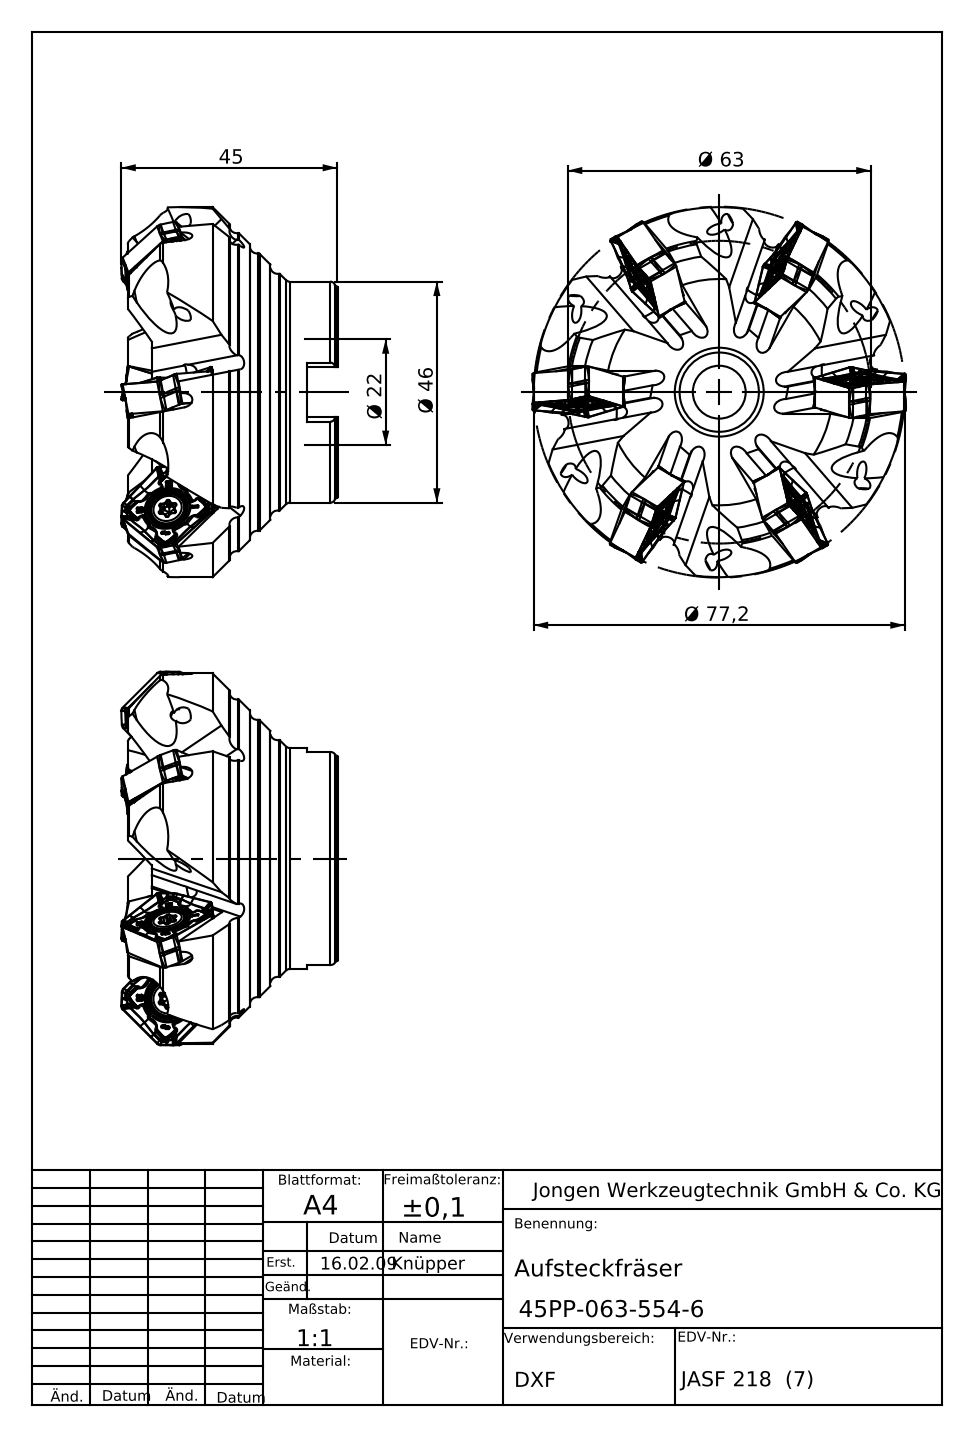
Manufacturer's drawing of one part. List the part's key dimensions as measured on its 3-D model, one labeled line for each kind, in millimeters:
Part name (STEP PRODUCT): 45PP-063-554-6
STEP written by: SolidWorks 2012 (AUTOMOTIVE_DESIGN)
Units: millimetres
Bodies: 1 solid, 298 faces (116 planar, 79 cylindrical, 103 other)
Overall size (bounding box): 78.3 × 78.3 × 45.1
Volume: 114 540 mm³ · Surface area: 23 620 mm²
Round holes (diameter × count): ⌀3 ×6, ⌀11 ×1, ⌀16.5 ×1, ⌀22 ×1, ⌀22.15 ×1, ⌀22.3 ×1
Round bosses / shafts (diameter × count): ⌀78.3 ×1, ⌀46 ×1
Partial cylindrical surfaces — rounded edges, fillets, slot ends (radius × count): R1.5 ×18, R1.5 ×6, R1.65 ×6, R38.5 ×1
Main face-to-face distances: 38.65, 45.1, 6.45, 6.3, 32.35, 38.8, 5.55, 22, 15.7, 16.65
